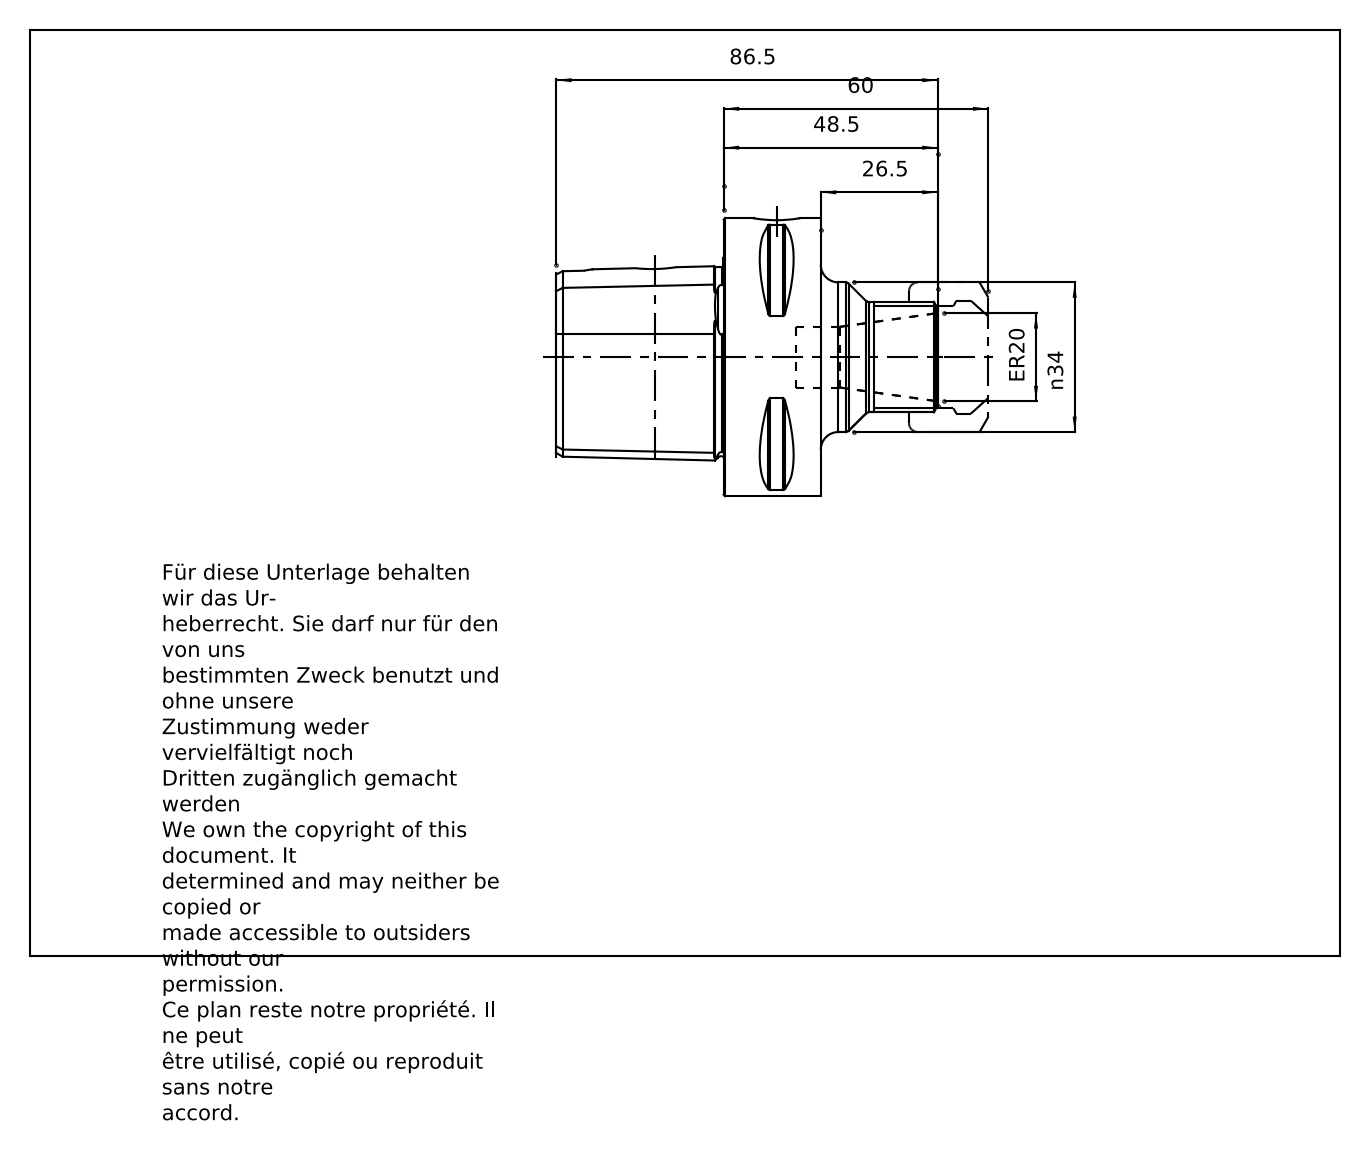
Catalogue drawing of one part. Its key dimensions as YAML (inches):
part_name: "CC6-025-20; 83-912-20; CC6-025-20_ASM"
step_written_by: "PRO/ENGINEER BY PARAMETRIC TECHNOLOGY CORPORATION, 2010430 (CONFIG_CONTROL_DESIGN)"
units: inches
bodies: {solids: 2, faces: 152, planar: 31, cylindrical: 37, other: 84}
overall_size: [3.858, 2.48, 2.48]
volume: 7.458
surface_area: 43.6
round_holes:
  - {diameter: 0.167, count: 1}
  - {diameter: 0.319, count: 1}
  - {diameter: 0.395, count: 1}
  - {diameter: 0.531, count: 1}
  - {diameter: 0.709, count: 1}
  - {diameter: 1.103, count: 1}
  - {diameter: 1.26, count: 1}
round_bosses_or_shafts:
  - {diameter: 2.48, count: 1}
  - {diameter: 1.339, count: 1}
  - {diameter: 0.984, count: 1}
  - {diameter: 0.787, count: 1}
partial_cylinders:
  - {radius: 0.02, count: 8}
  - {radius: 0.236, count: 1}
face_to_face_distances: [0.748, 0.866, 1.496, 2.362, 1.614, 1.181, 3.11, 3.858, 1.063, 2.343]
hole_center_spacings: [1.083]
